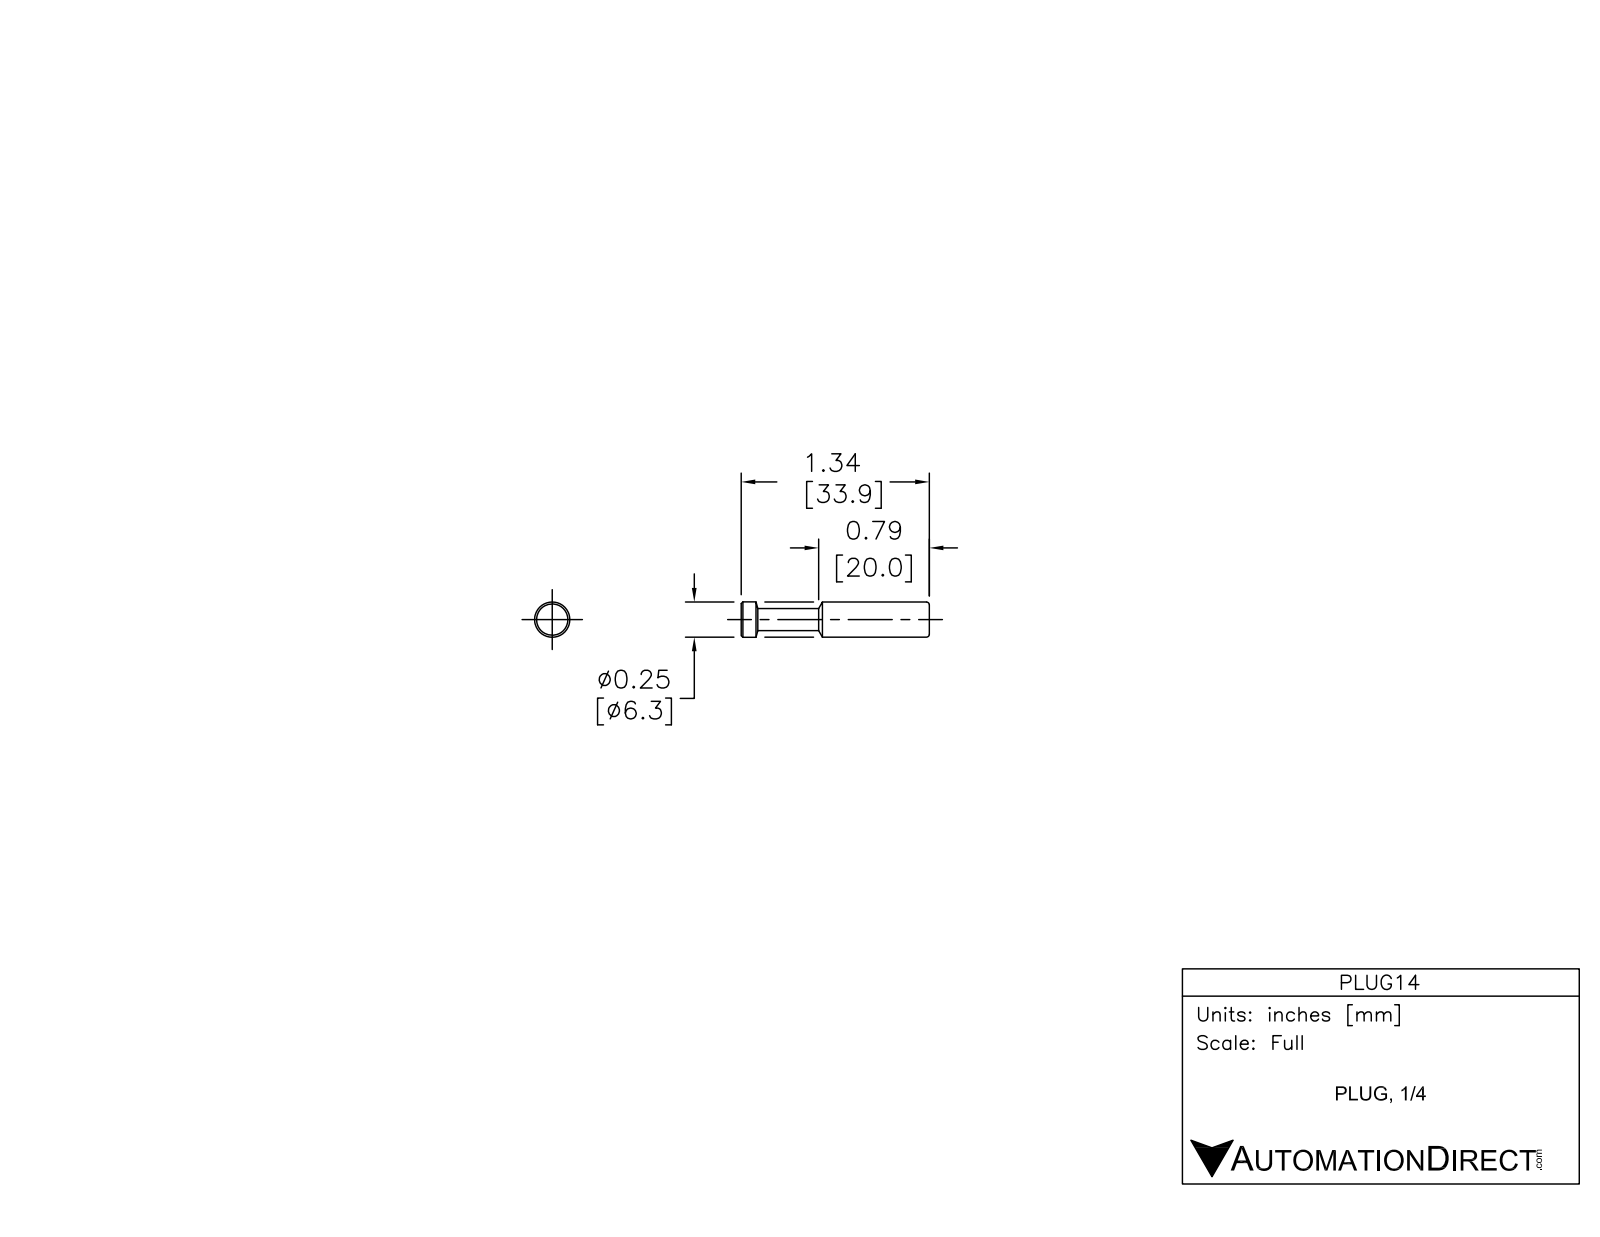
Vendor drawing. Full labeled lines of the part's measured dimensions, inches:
Part name (STEP PRODUCT): PLUG14
STEP written by: SolidWorks 2015 (AUTOMOTIVE_DESIGN)
Units: inches
Bodies: 1 solid, 16 faces (2 planar, 6 cylindrical, 8 other)
Overall size (bounding box): 1.339 × 0.252 × 0.252
Volume: 0.052 in³ · Surface area: 1.047 in²
Round bosses / shafts (diameter × count): ⌀0.252 ×1, ⌀0.25 ×1, ⌀0.157 ×1
Main face-to-face distances: 1.339
